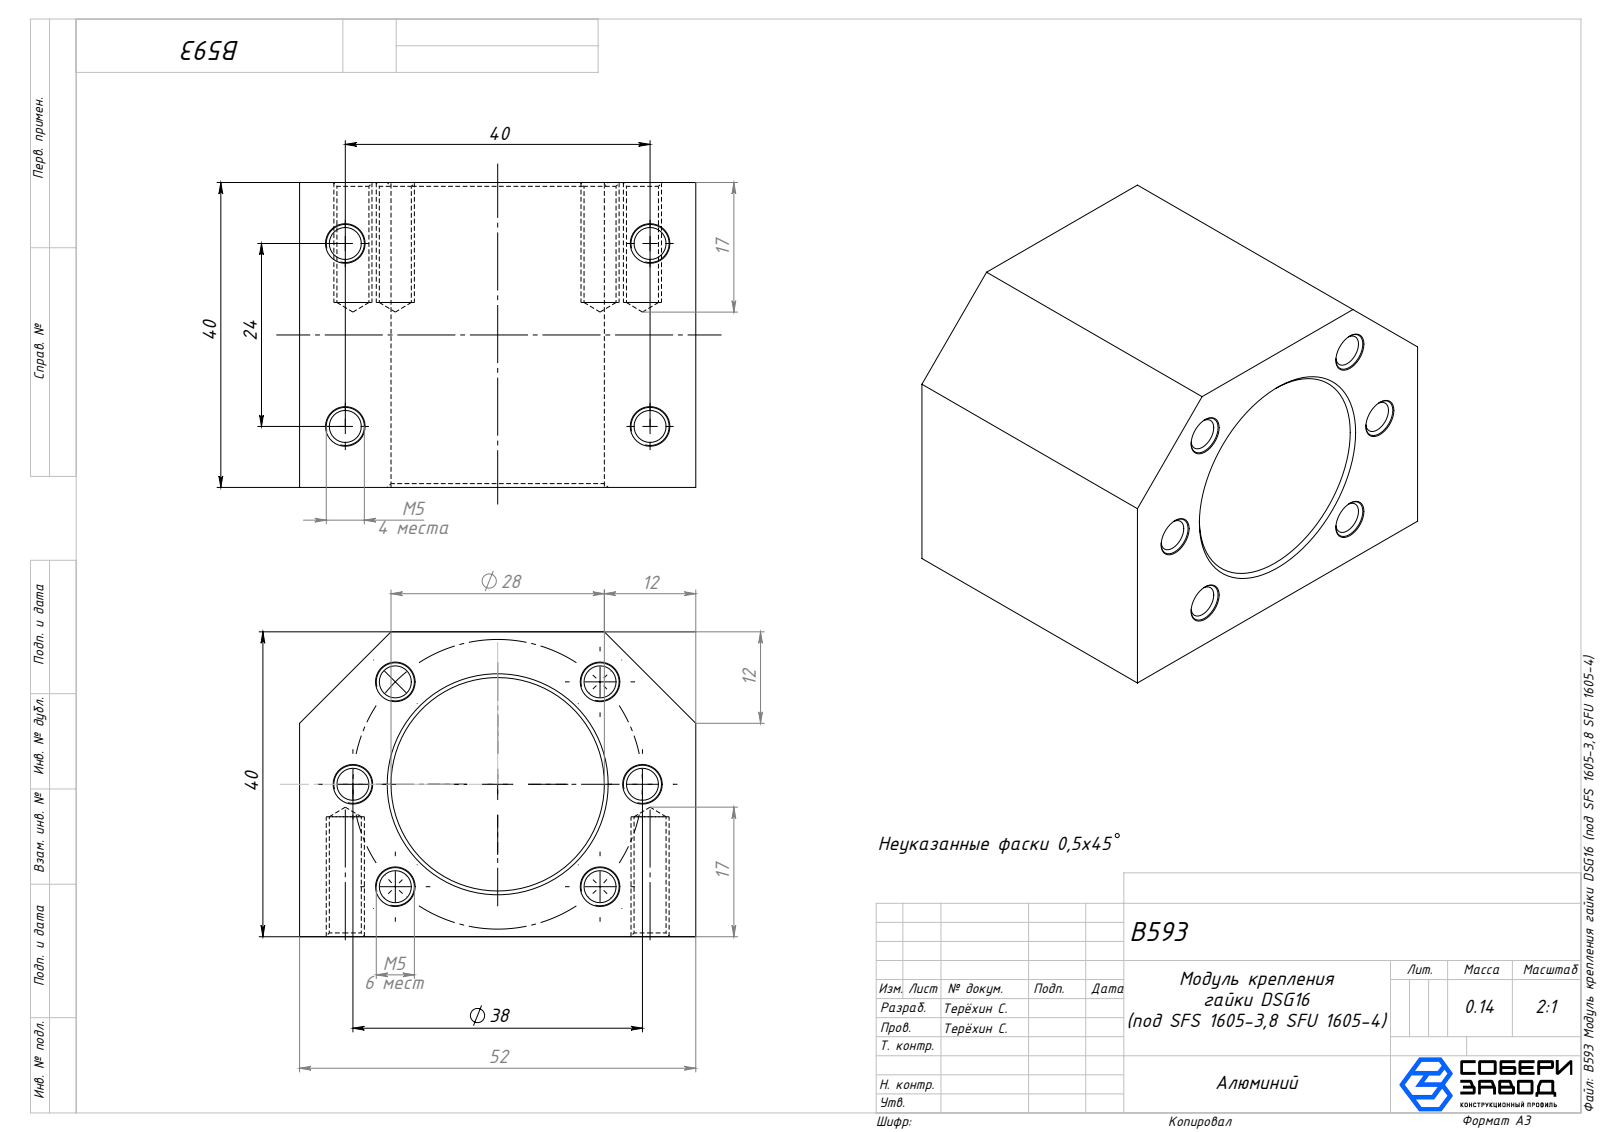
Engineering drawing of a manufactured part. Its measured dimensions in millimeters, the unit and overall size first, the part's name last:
Units: millimetres
Overall size (bounding box): 52 × 40 × 40
Round holes (diameter × count): ⌀4.2 ×10, ⌀28 ×1
Main face-to-face distances: 40, 52
Hole centre spacings: 14.54, 19.01, 26.88, 35.11, 19, 24, 38.01, 40
Volume: 50 531 mm³ · Surface area: 14 970 mm²
Bodies: 1 solid, 74 faces (8 planar, 22 cylindrical, 44 other)
Part name (STEP PRODUCT): B593 Модуль крепления гайки DSG16 (под SFS 1505-3,8 1605-4)_DSG16H; B593 Модуль крепления гайки DSG16 (под SFS 1505-3,8 1605-4)
STEP written by: SolidWorks 2025 (CONFIG_CONTROL_DESIGN)
